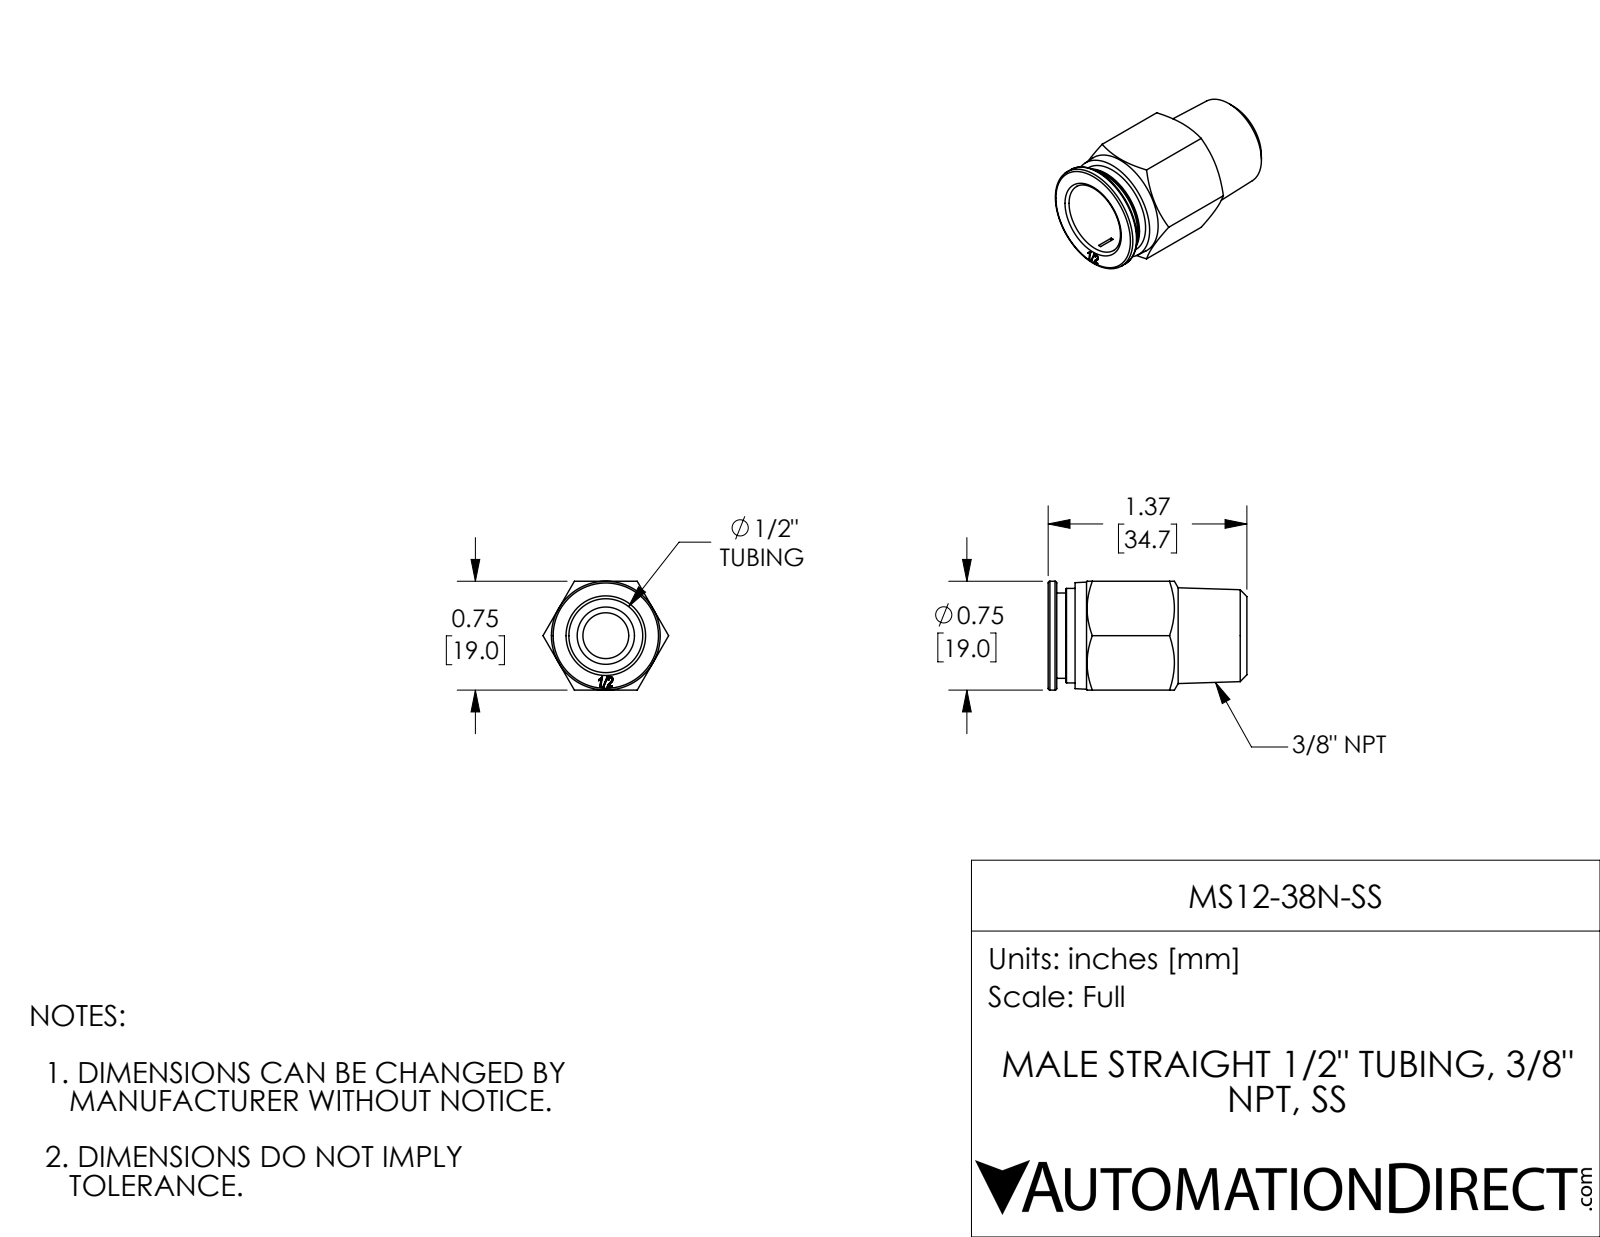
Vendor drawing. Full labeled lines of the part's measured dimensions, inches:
Part name (STEP PRODUCT): MS12-38N-SS
STEP written by: SolidWorks 2017 (AUTOMOTIVE_DESIGN)
Units: inches
Bodies: 1 solid, 87 faces (35 planar, 12 cylindrical, 40 other)
Overall size (bounding box): 1.366 × 0.864 × 0.748
Volume: 0.336 in³ · Surface area: 6.133 in²
Round holes (diameter × count): ⌀0.315 ×1, ⌀0.508 ×1, ⌀0.594 ×1
Round bosses / shafts (diameter × count): ⌀0.748 ×1, ⌀0.65 ×1, ⌀0.587 ×1
Main face-to-face distances: 0.748, 0.059, 1.307, 1.366, 1.181, 0.126, 0.185, 0.516, 0.665, 0.791
